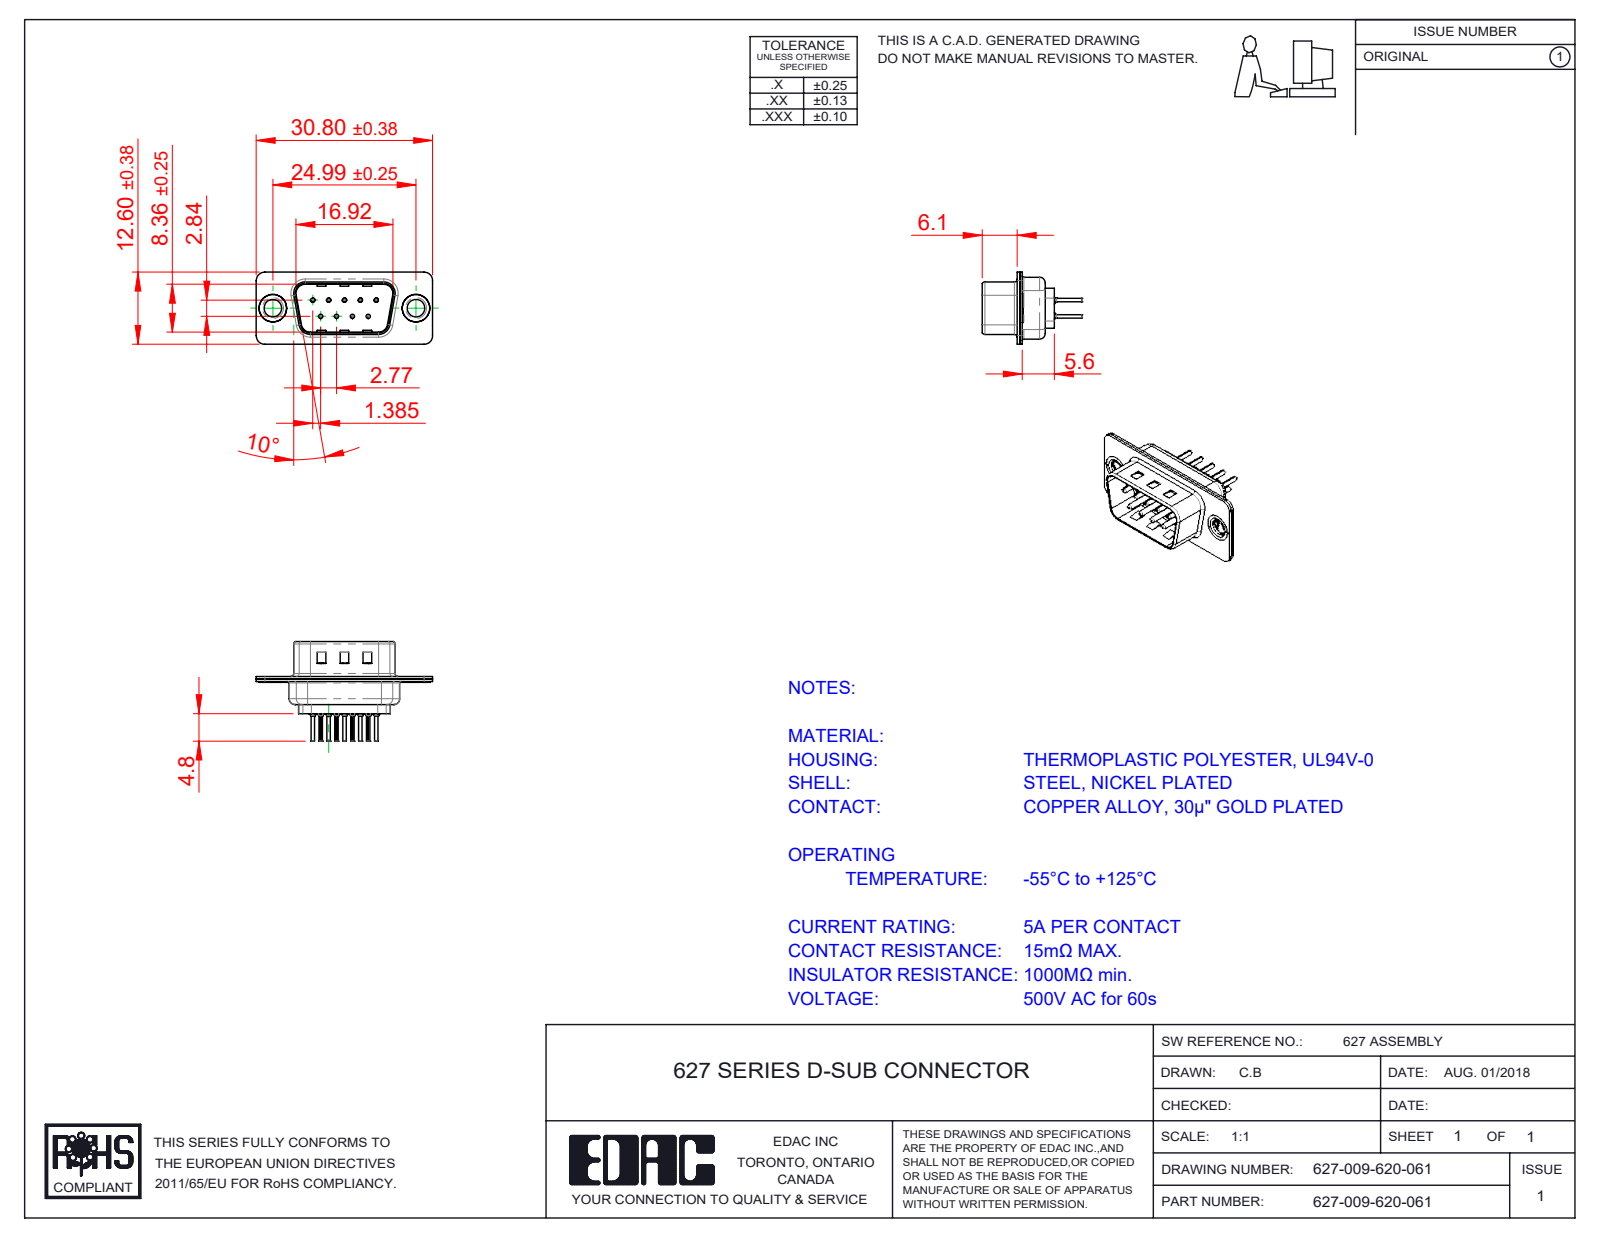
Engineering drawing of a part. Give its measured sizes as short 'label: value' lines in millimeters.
name: 627 Contact Row 1_20L; 627 Contact Row 2_20L; 627 Shell Rear_09 Contacts; 627 Housing_09 LP (+3 more)
written by: SolidWorks 2020 (CONFIG_CONTROL_DESIGN)
unit: mm
bodies: 14 solids, 1160 faces (323 planar, 446 cylindrical, 391 other)
size: 30.8 × 17.3 × 12.6
volume: 1 234 mm³; area: 3 789 mm²
holes: 9× ⌀0.2, 9× ⌀0.35, 9× ⌀1.1, 9× ⌀1.6, 2× ⌀3.05, 2× ⌀4, 2× ⌀4.8
bosses: 9× ⌀2, 9× ⌀1.5, 9× ⌀0.75, 9× ⌀0.6, 2× ⌀5, 2× ⌀4.9, 2× ⌀3.55
rounds: 18× R0.1, 18× R1.5, 12× R2, 8× R0.5, 8× R1.6, 4× R0.25, 4× R0.6, 4× R0.65
face distances: 0.45, 0.4, 0.9, 0.82, 9.58, 1.4, 0.5, 8.76, 1.5, 5.6
hole spacings: 3.16, 2.77, 5.54, 5.03, 5.04, 8.31, 7.48, 7.49
